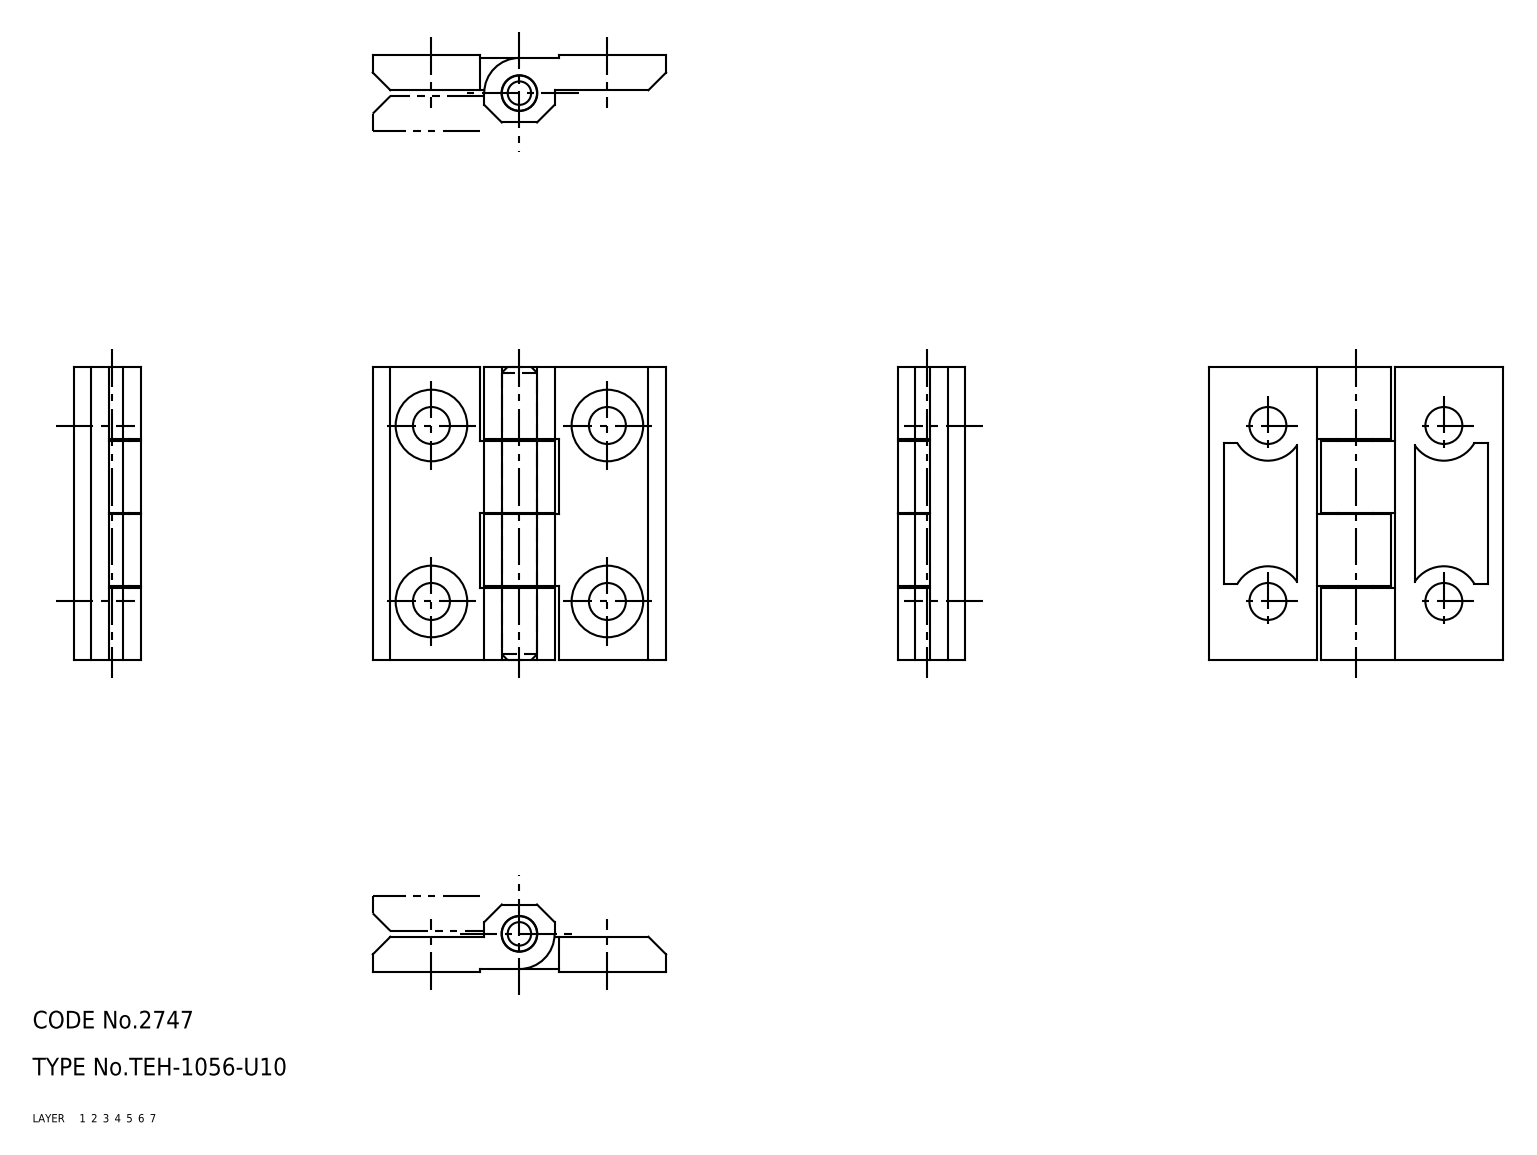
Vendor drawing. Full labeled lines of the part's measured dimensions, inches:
Part name (STEP PRODUCT): shaft; hinge pieces_B; hinge pieces_A; TEH_1056_U10_2821_36
STEP written by: CADfix (AUTOMOTIVE_DESIGN)
Units: inches
Bodies: 3 solids, 94 faces (0 planar, 0 cylindrical, 94 other)
Overall size (bounding box): 1.969 × 1.969 × 0.453
Volume: 0.831 in³ · Surface area: 15.23 in²
